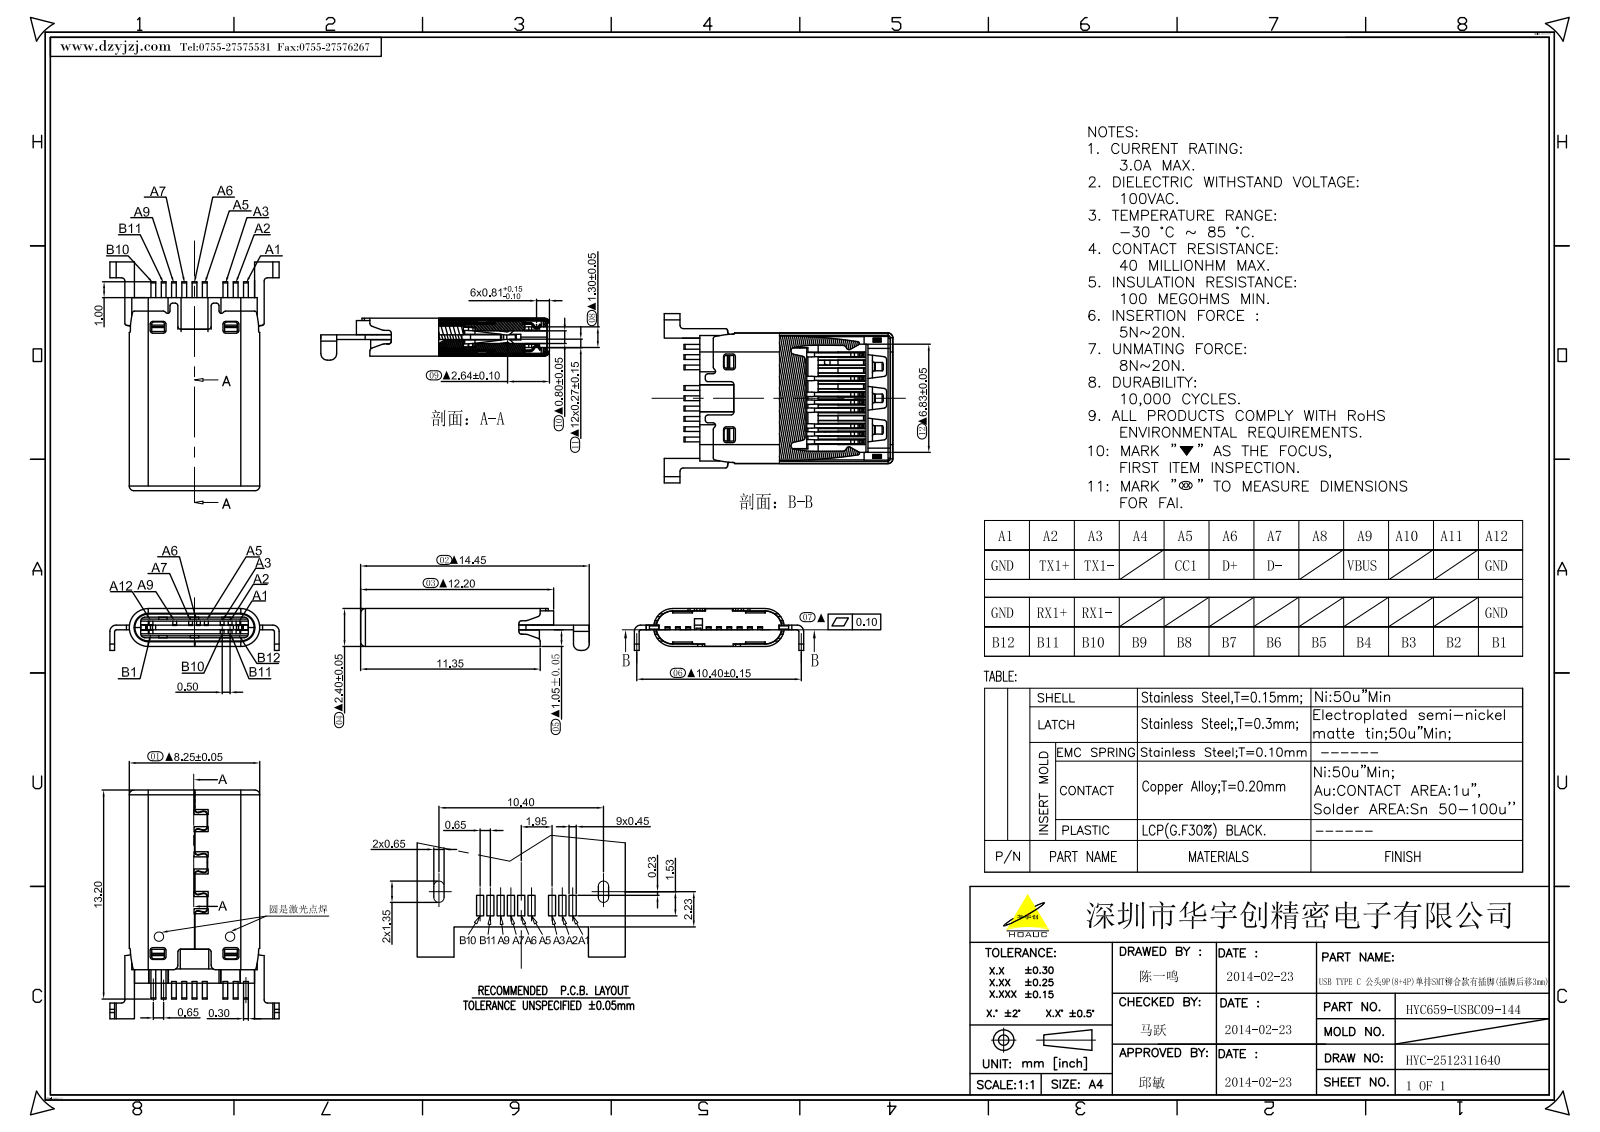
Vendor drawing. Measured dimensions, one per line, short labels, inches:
name: TANPIAN-PLASTIC_1_2__2_1_1_2_12
written by: CREO PARAMETRIC BY PTC INC, 2022073 (CONFIG_CONTROL_DESIGN)
unit: in
bodies: 1 solid, 520 faces (360 planar, 156 cylindrical, 4 other)
size: 0.569 × 0.421 × 0.104
volume: 0.011 in³; area: 0.646 in²
rounds: 32× R0.006, 14× R0.008, 8× R0.004, 8× R0.012, 6× R0.007, 6× R0.009, 6× R0.01, 4× R0.016
face distances: 0.031, 0.094, 0.063, 0.041, 0.022, 0.053, 0.02, 0.073, 0.035, 0.051
